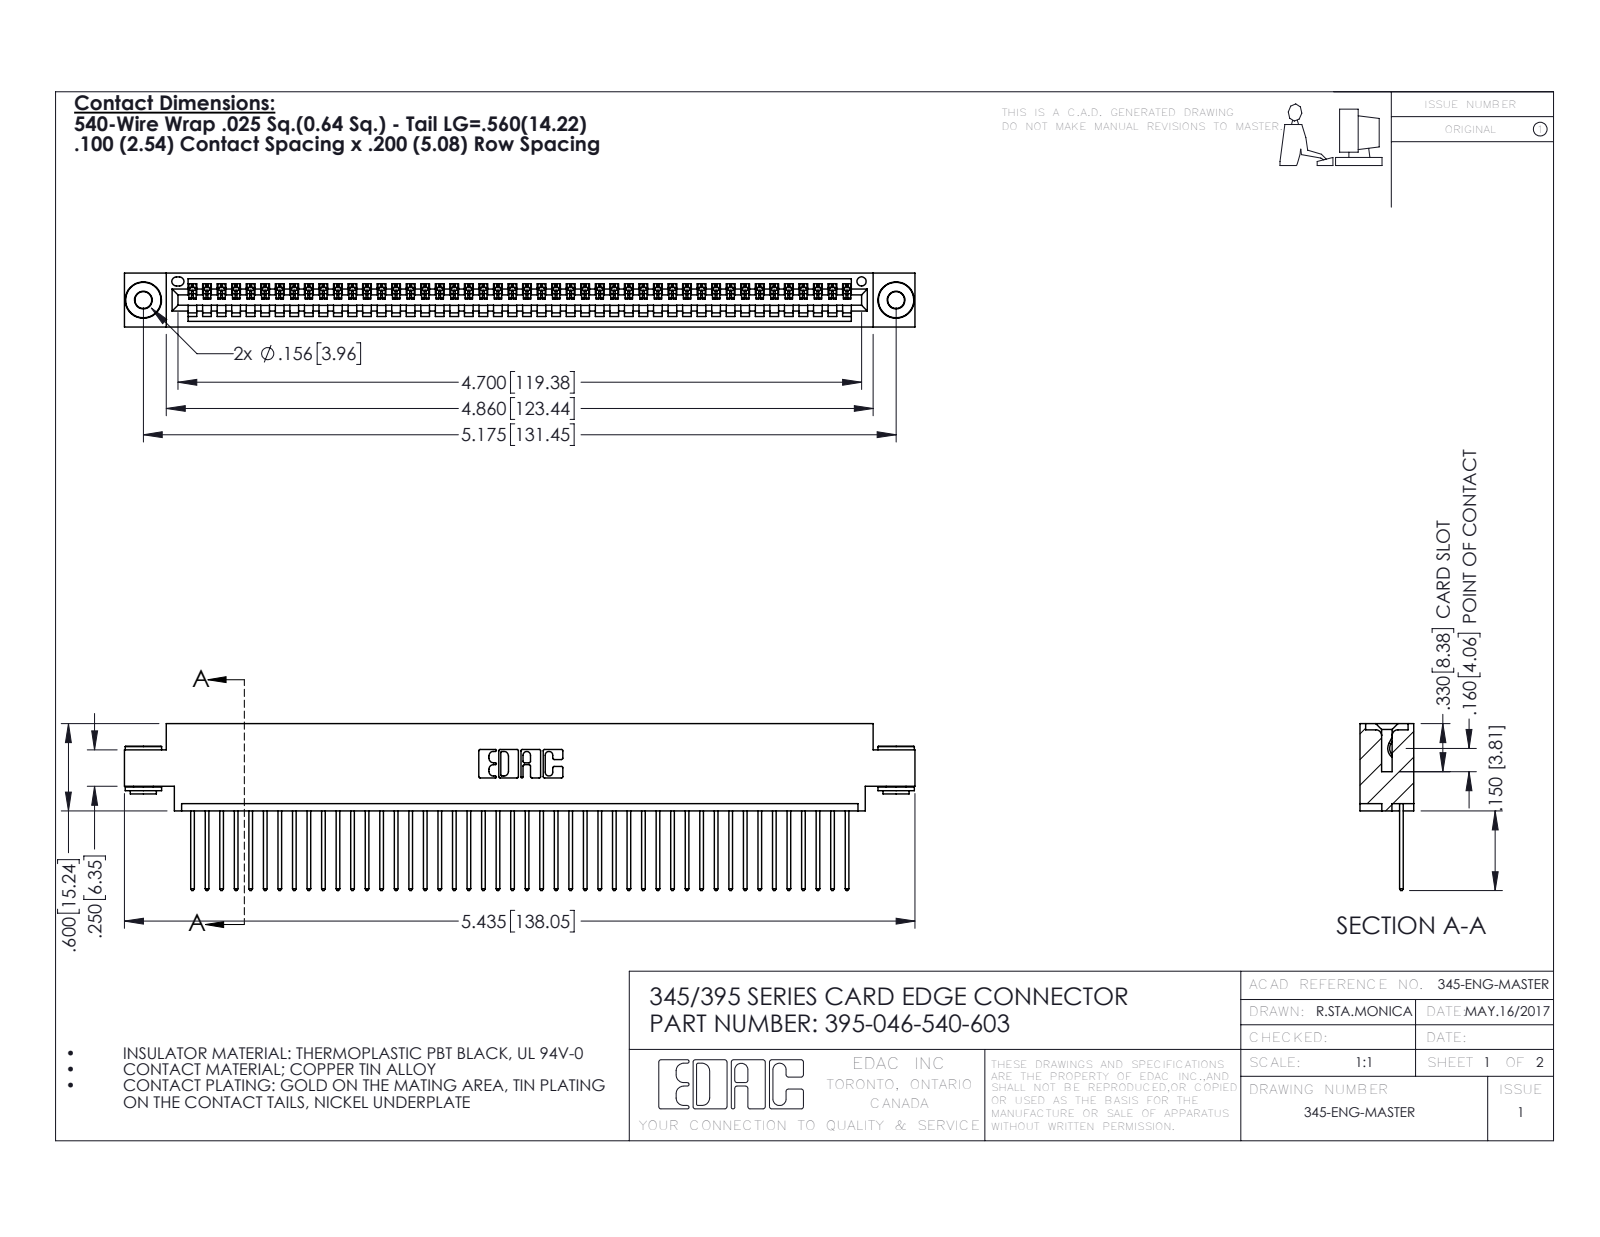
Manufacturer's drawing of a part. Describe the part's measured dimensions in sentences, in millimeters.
The part is named "345-292-001_345-293-140; 345-250-002_345-250-002-102; 345 Part_0.170 Offset - 0.156 Dia-TH; 395-046-540-603". Its 3-D file was written by "SolidWorks 2016 (CONFIG_CONTROL_DESIGN)". It is 49 solids with 2836 faces: 1934 planar, 894 cylindrical and 8 other. Overall it measures 138 by 29.1 by 9.4 millimeters. Its volume is 13 100 cubic millimeters and its surface area 18 270 square millimeters. Round holes: 2 of diameter 2.9, 2 of diameter 4, 1 of diameter 1.6. Round bosses or shafts: 2 of diameter 6.4, 2 of diameter 4.6, 2 of diameter 3.5. Partial cylindrical surfaces (rounded edges, fillets, slot ends): 92 of radius 0.2, 92 of radius 0.3, 22 of radius 0.3, 6 of radius 0.2, 6 of radius 0.8, 3 of radius 0.7, 2 of radius 0.8, 2 of radius 1. The main face-to-face distances are 1.8, 7.6, 9.4, 2.5, 6.9, 0.6, 5.1, 5.7, 4.4, 3.8. The hole center spacings are 6.9, 125.5, 131.4.
